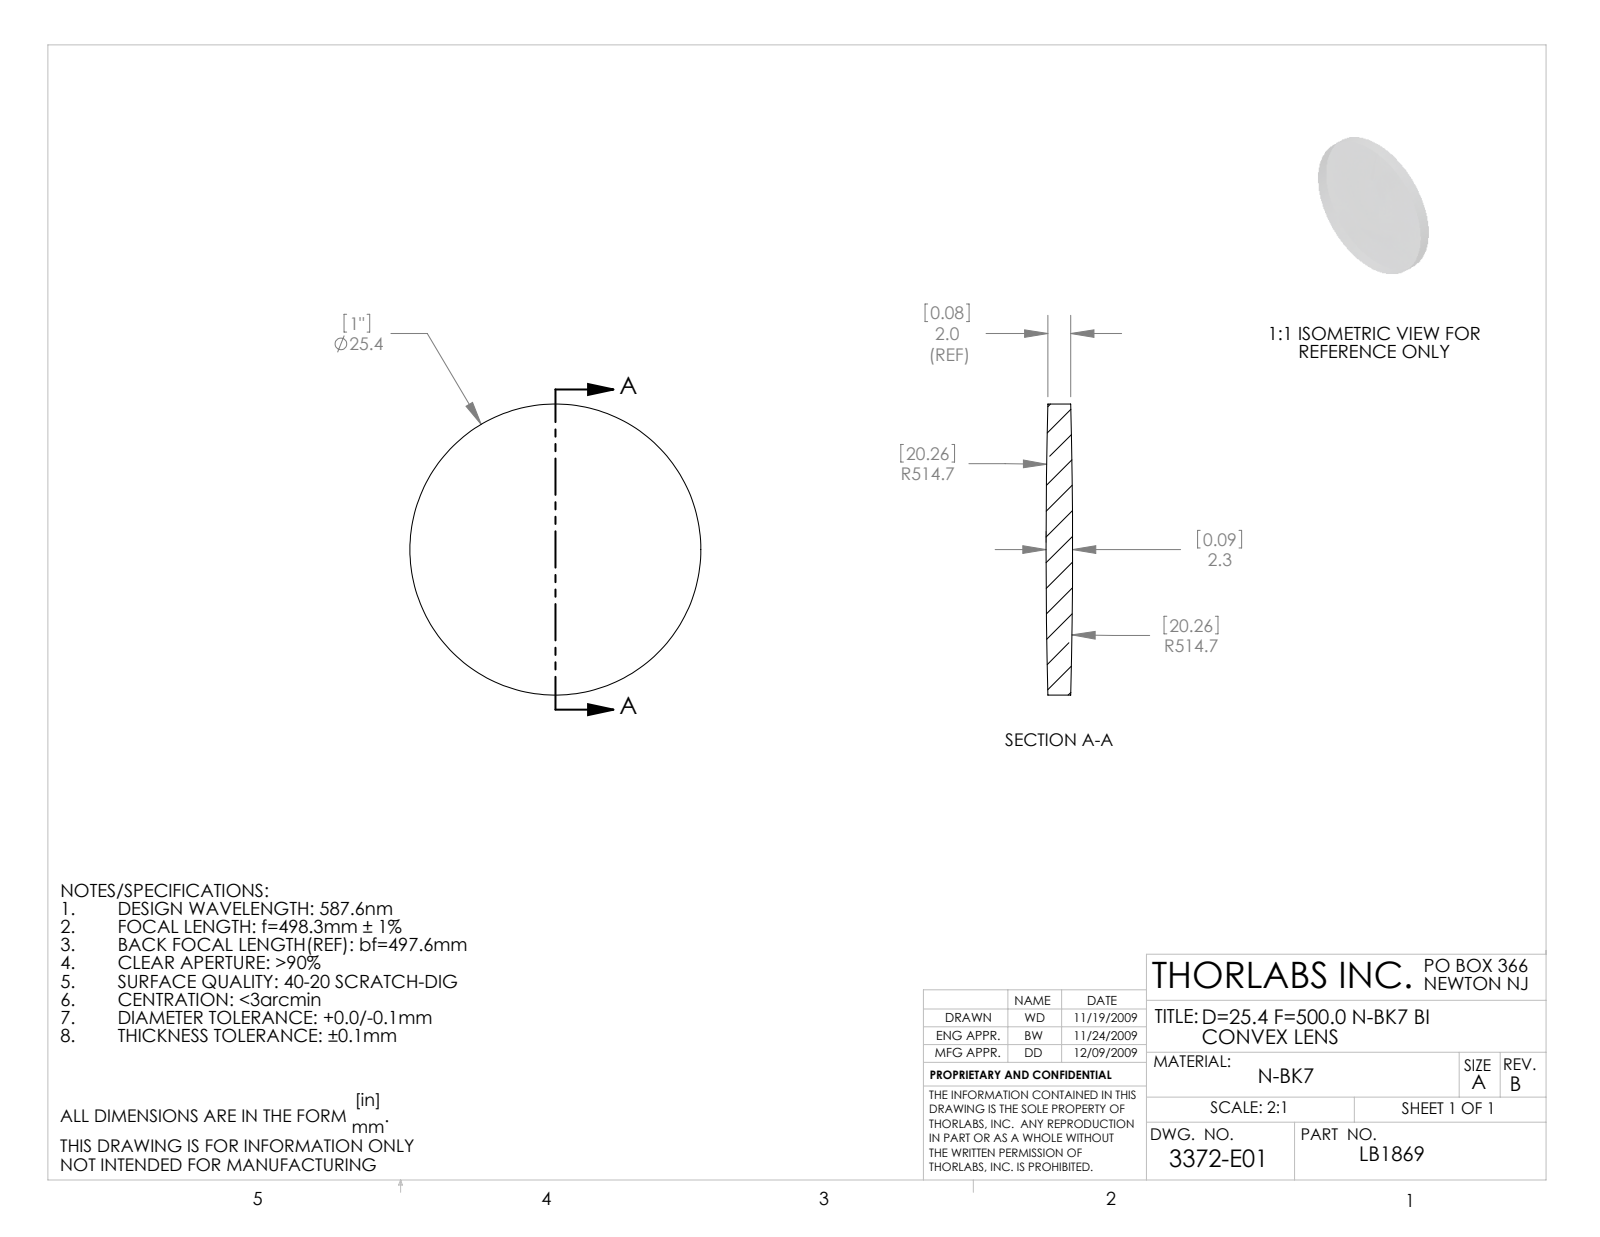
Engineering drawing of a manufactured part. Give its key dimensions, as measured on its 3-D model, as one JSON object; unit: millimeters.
{"part_name": "3372-E0W", "step_written_by": "SolidWorks 2009 (AUTOMOTIVE_DESIGN)", "units": "millimeters", "bodies": {"solids": 1, "faces": 6, "planar": 0, "cylindrical": 2, "other": 4}, "overall_size": [25.4, 25.4, 2.31], "volume_mm3": 1091, "surface_area_mm2": 1173, "round_bosses_or_shafts": [[25.4, 1]]}
